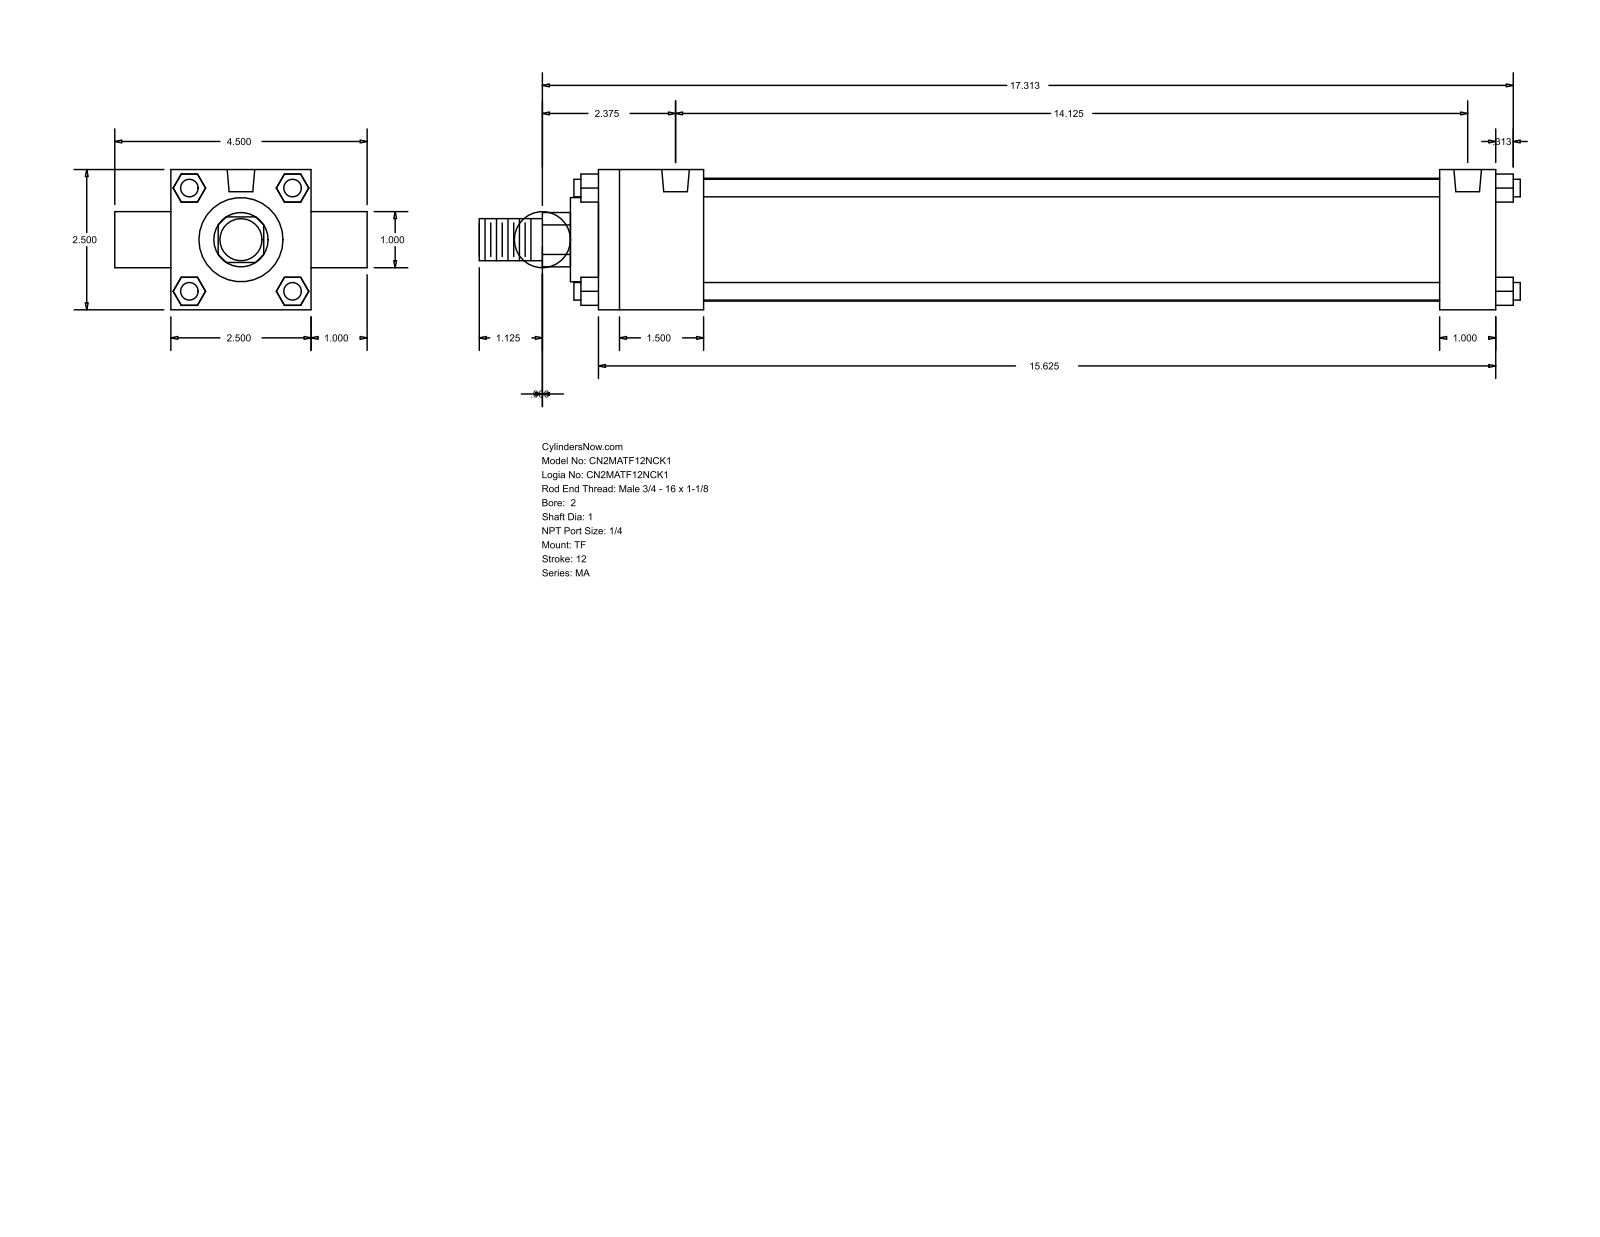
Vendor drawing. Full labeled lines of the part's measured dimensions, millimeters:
Part name (STEP PRODUCT): MA_TF__0200_1
STEP written by: GSSL Pune (CONFIG_CONTROL_DESIGN)
Units: millimetres
Bodies: 0 solids, 120 faces (92 planar, 28 cylindrical, 0 other)
Overall size (bounding box): 471.49 × 114.3 × 63.5
Round holes (diameter × count): ⌀7.94 ×3, ⌀12.49 ×2
Round bosses / shafts (diameter × count): ⌀7.94 ×4, ⌀25.4 ×2, ⌀55.63 ×1, ⌀38.1 ×1, ⌀19.05 ×1
Partial cylindrical surfaces — rounded edges, fillets, slot ends (radius × count): R12.29 ×1
Main face-to-face distances: 63.5, 25.4, 406.4, 12.7, 47.63, 381, 333.37, 358.77, 88.9, 23.37
Hole centre spacings: 358.77
